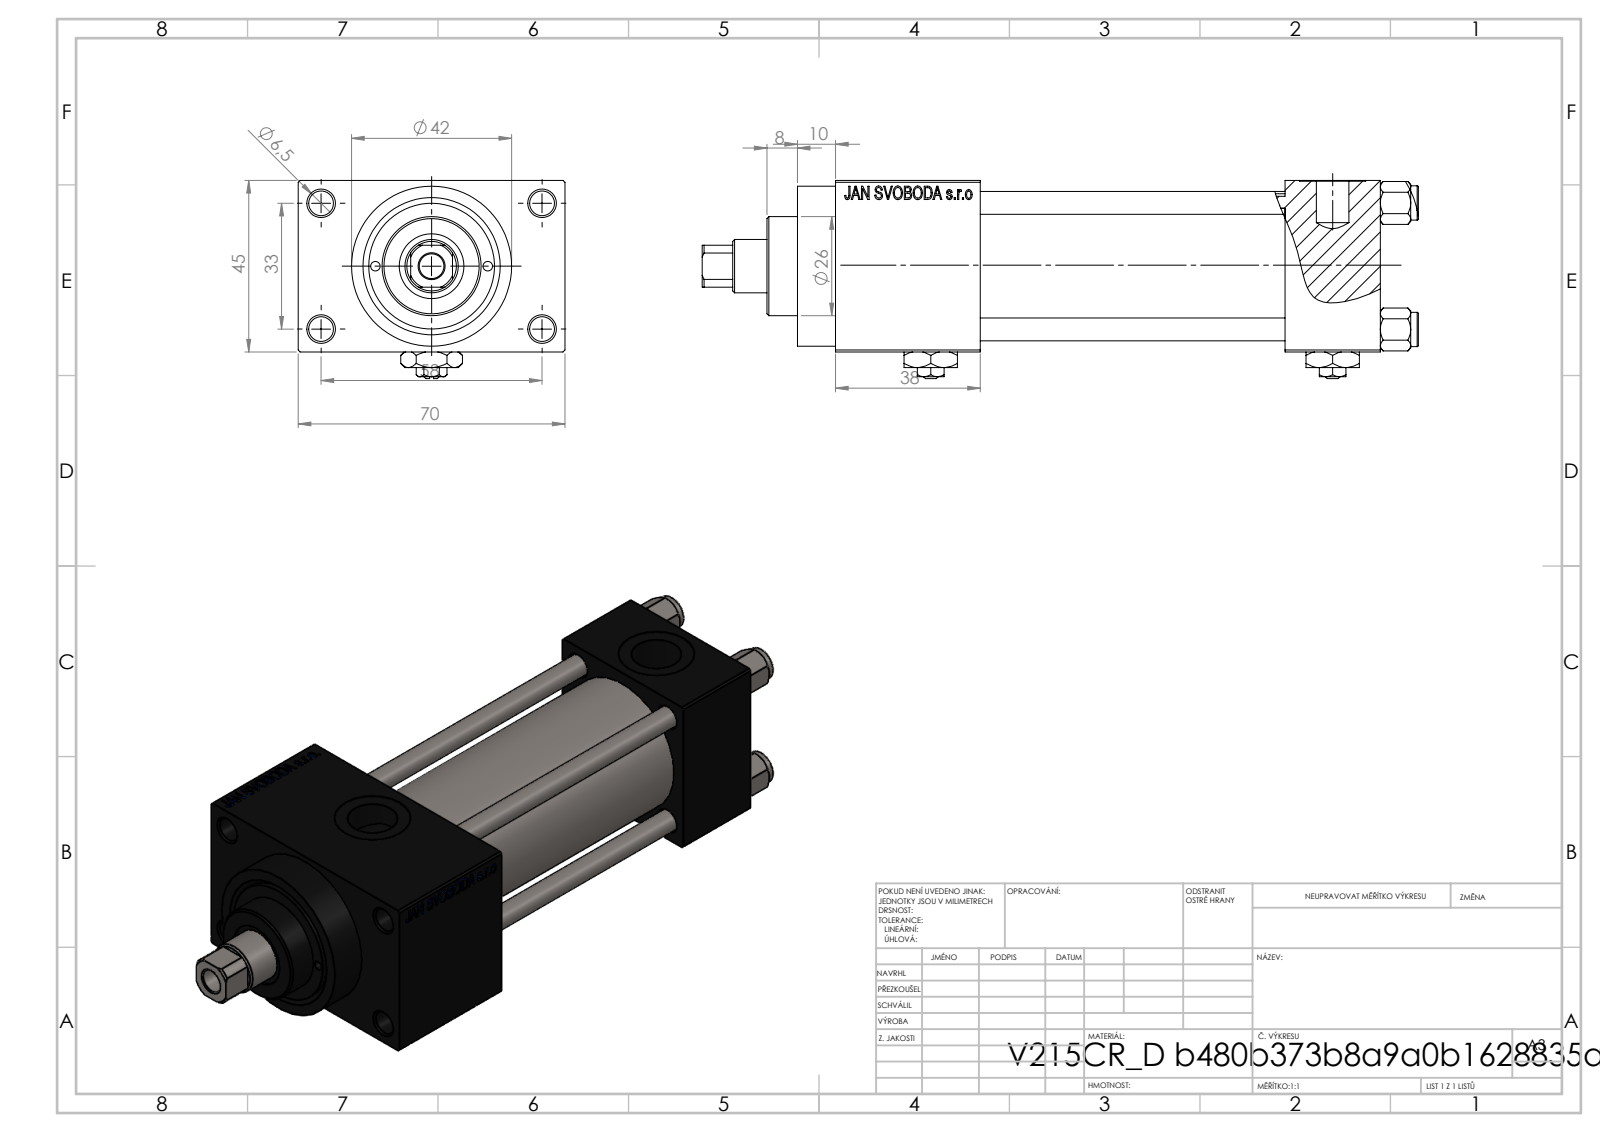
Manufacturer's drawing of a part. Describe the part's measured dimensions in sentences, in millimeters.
The part is named "NUT_M5_D; V215CR_D_TYCINKA; V215CR_VCP_D; Zatka_pro_OIL_PORT (+2 more)". Its 3-D file was written by "SolidWorks 2019 (CONFIG_CONTROL_DESIGN)". It is 13 solids with 1210 faces: 544 planar, 104 cylindrical and 562 other. Overall it measures 188 by 70 by 52 millimeters. Its volume is 248 436 cubic millimeters and its surface area 86 786 square millimeters. Round holes: 5 of diameter 6.5, 4 of diameter 6, 2 of diameter 2.5, 2 of diameter 7, 2 of diameter 13.16, 2 of diameter 20, 1 of diameter 14, 1 of diameter 17, 1 of diameter 24, 1 of diameter 32, 1 of diameter 33. Round bosses or shafts: 4 of diameter 9, 1 of diameter 42, 1 of diameter 38, 1 of diameter 26. Partial cylindrical surfaces (rounded edges, fillets, slot ends): 1 of radius 6.5. The main face-to-face distances are 45, 25, 12.5, 57.5, 80, 105, 118, 70, 38, 143. The hole center spacings are 12.4, 16.7, 21.8, 23.48, 33.2, 33.37, 35.35, 35.47.
